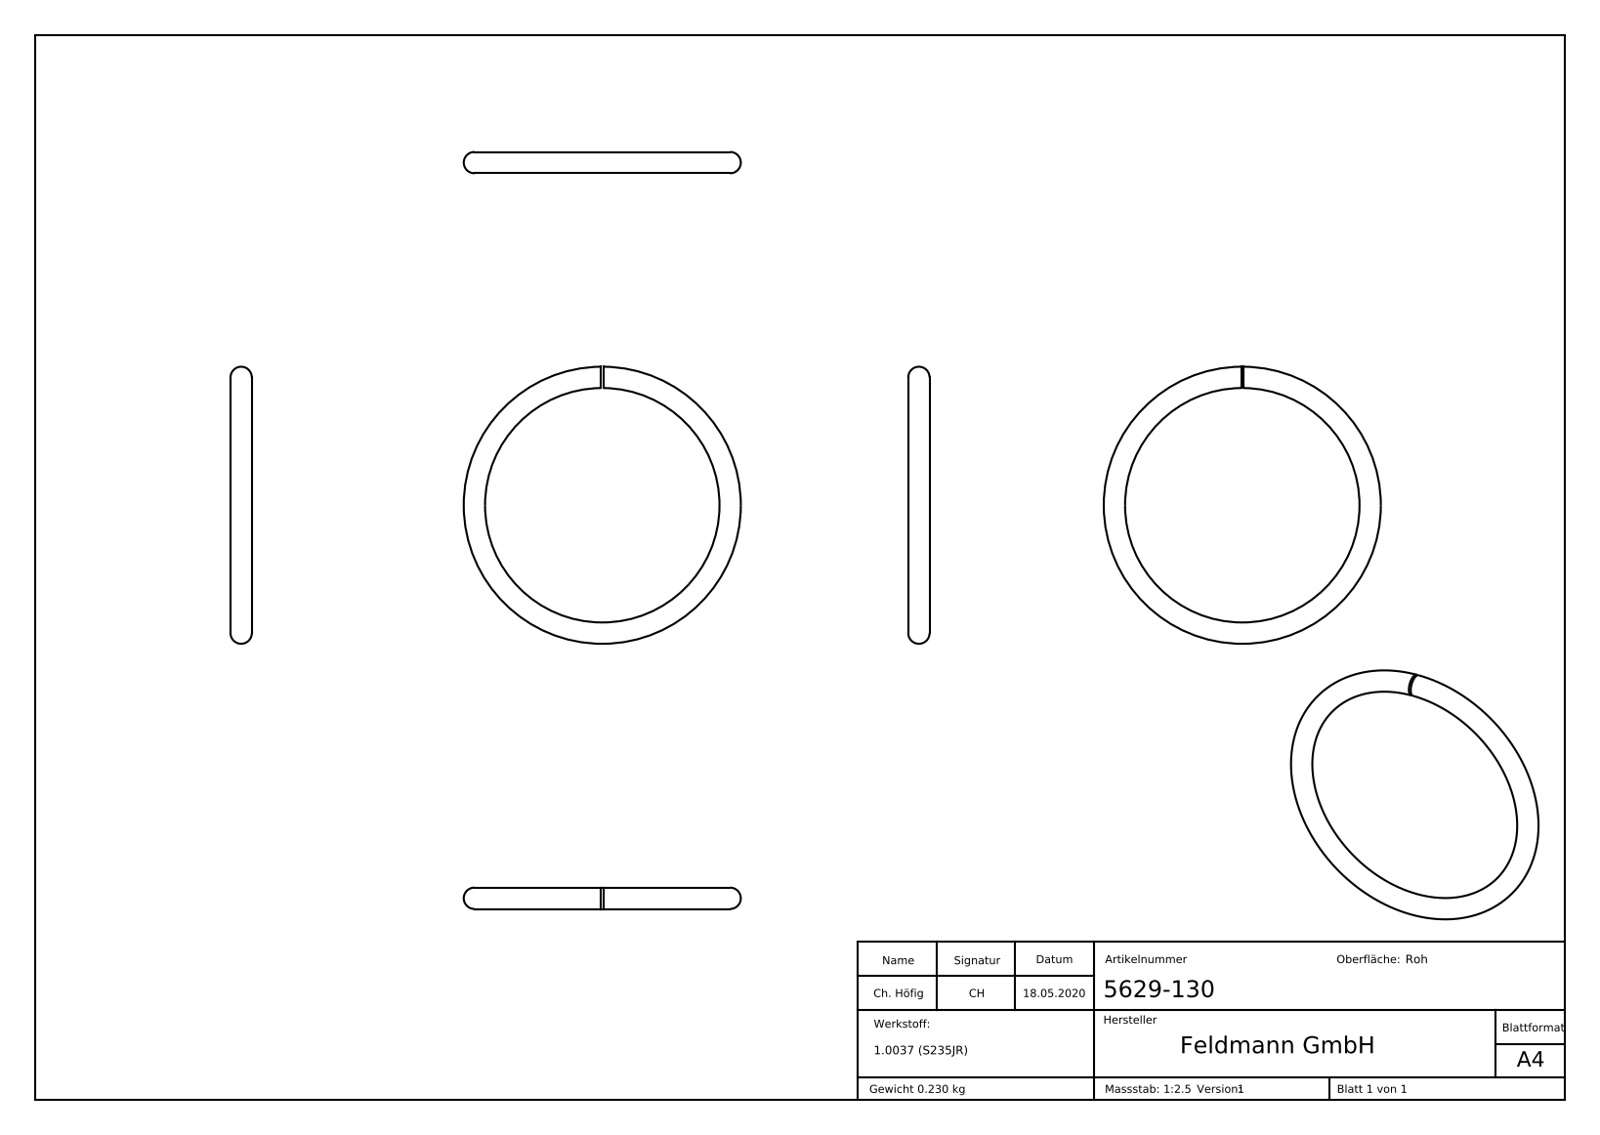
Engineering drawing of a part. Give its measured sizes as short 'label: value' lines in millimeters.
name: 5629-130
written by: SolidWorks 2015 (CONFIG_CONTROL_DESIGN)
unit: mm
bodies: 1 solid, 213 faces (109 planar, 0 cylindrical, 104 other)
size: 130 × 130 × 10
volume: 29 521 mm³; area: 11 996 mm²
face distances: 1, 1.5, 0.5, 1.78, 2.12, 0.83, 2.45, 0.99, 2.77, 0.67
